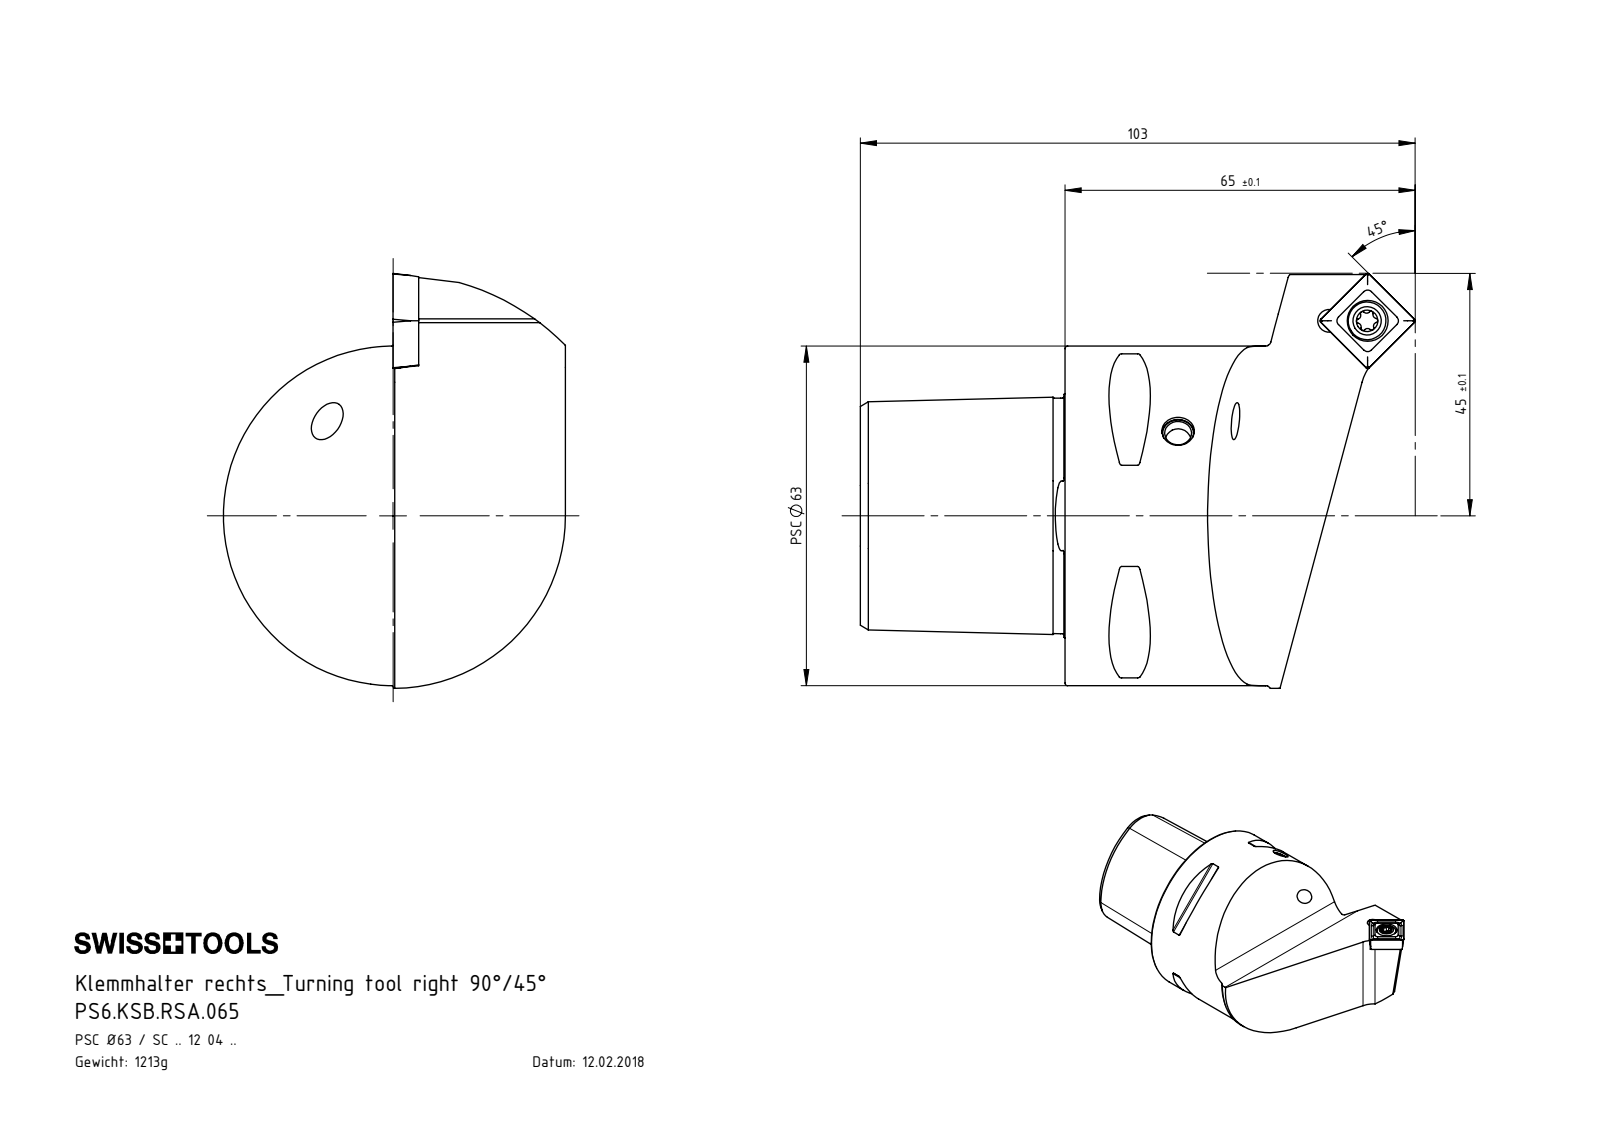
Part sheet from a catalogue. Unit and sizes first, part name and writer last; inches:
Units: inches
Overall size (bounding box): 4.055 × 3.031 × 2.5
Round holes (diameter × count): ⌀0.165 ×2, ⌀0.197 ×2, ⌀0.157 ×1, ⌀0.217 ×1, ⌀0.299 ×1, ⌀0.319 ×1, ⌀0.709 ×1, ⌀1.102 ×1, ⌀1.26 ×1
Round bosses / shafts (diameter × count): ⌀2.48 ×1, ⌀0.276 ×1, ⌀0.236 ×1, ⌀0.197 ×1
Partial cylindrical surfaces — rounded edges, fillets, slot ends (radius × count): R0.02 ×8, R0.015 ×6, R0.027 ×3, R0.027 ×3, R0.236 ×2, R0.354 ×1, R1.26 ×1, R1.772 ×1
Main face-to-face distances: 1.496, 1.248, 0.98, 1.063, 0.433, 1.072, 0.176, 2.197, 1.488, 0.425
Hole centre spacings: 0.278, 0.283, 1.083, 2.038, 2.245, 2.249, 2.912, 3.158
Volume: 9.431 in³ · Surface area: 43.61 in²
Bodies: 5 solids, 269 faces (52 planar, 68 cylindrical, 149 other)
Part name (STEP PRODUCT): PS6-KSB.RSA.065_A_Fertigbearbeitung; KVT_MB_600_060; WCC-ER2.001.010_A; SCMT120404 (+1 more)
STEP written by: SolidWorks 2017 (AUTOMOTIVE_DESIGN)
